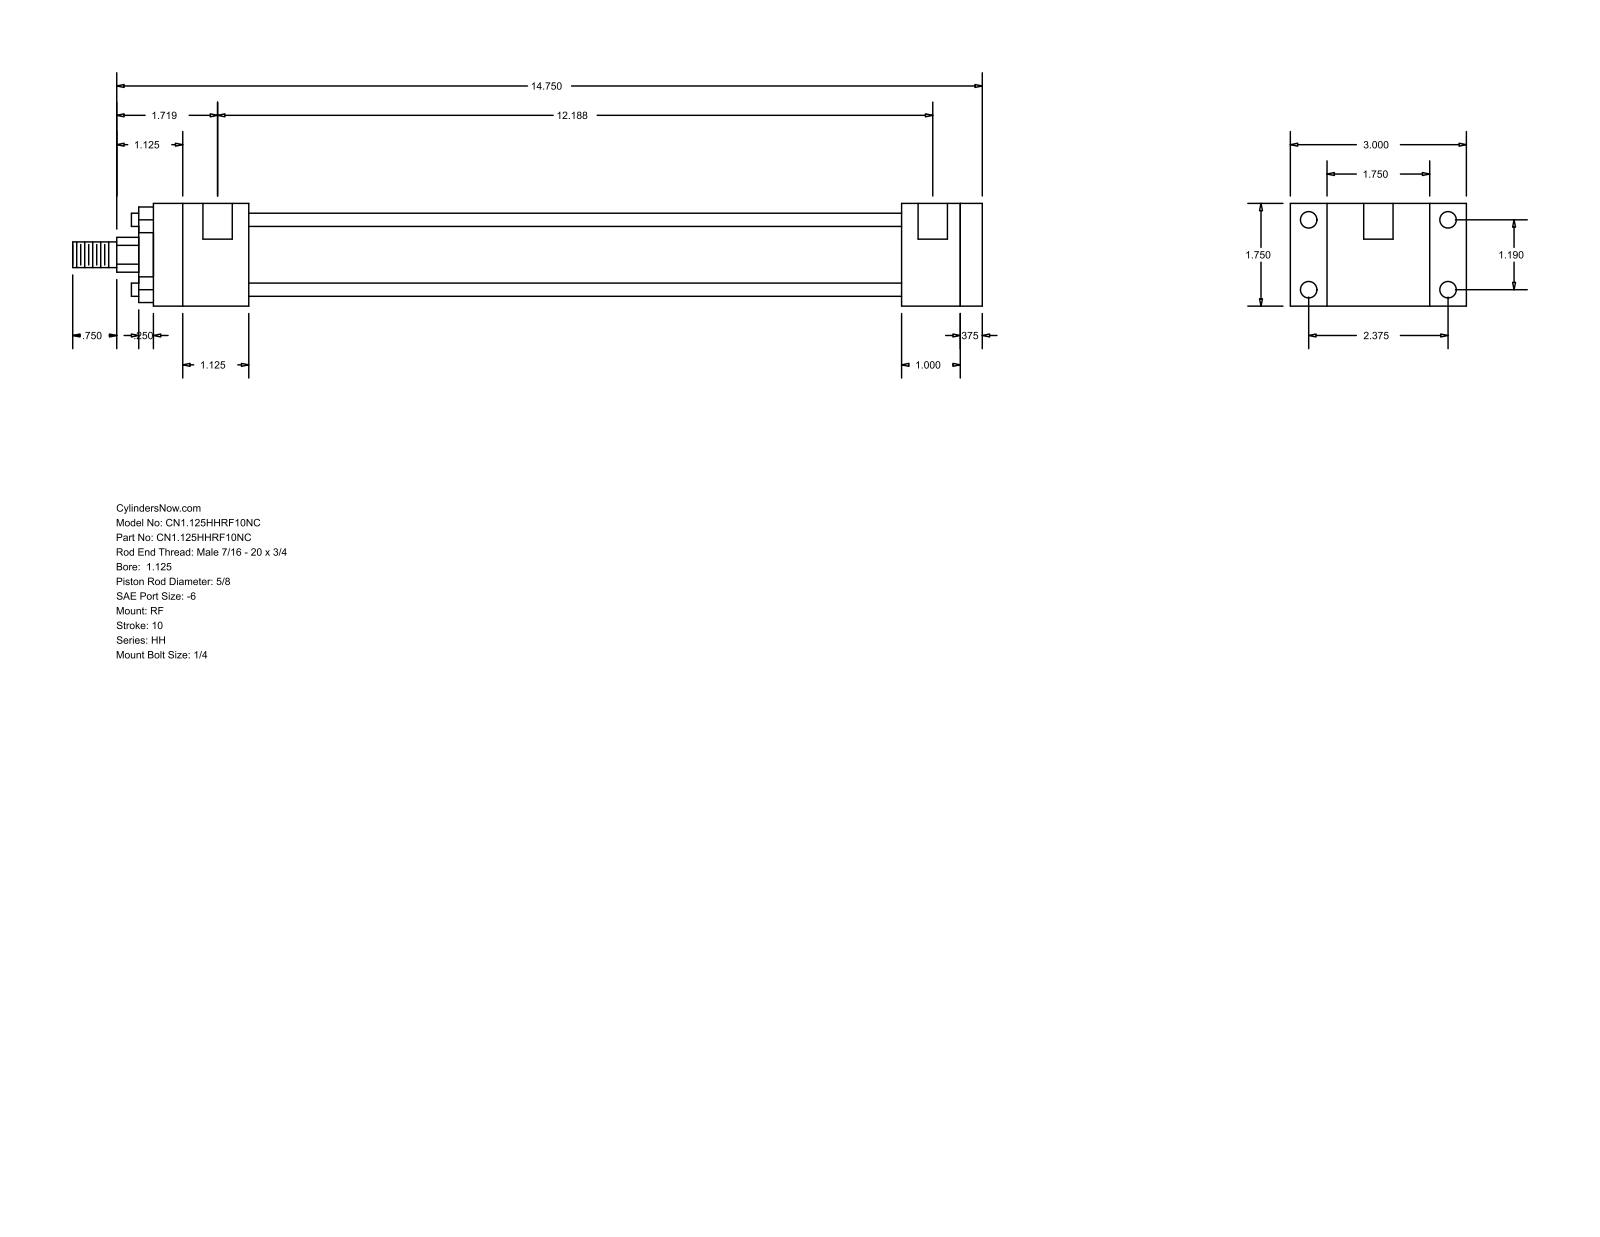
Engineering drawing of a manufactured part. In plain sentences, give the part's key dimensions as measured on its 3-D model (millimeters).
The part is named "HH_RF__0112_0.625". Its 3-D file was written by "GSSL Pune (CONFIG_CONTROL_DESIGN)". It is 0 solids with 92 faces: 64 planar, 28 cylindrical and 0 other. Overall it measures 393.7 by 76.2 by 44.45 millimeters. Round holes: 4 of diameter 5.56, 4 of diameter 7.14, 2 of diameter 12.7. Round bosses or shafts: 4 of diameter 5.71, 1 of diameter 34.92, 1 of diameter 28.57, 1 of diameter 15.88, 1 of diameter 11.11. Partial cylindrical surfaces (rounded edges, fillets, slot ends): 1 of radius 7.54. The main face-to-face distances are 44.46, 9.53, 358.77, 15.87, 307.97, 317.5, 282.58, 25.39, 34.92, 41.27. The hole center spacings are 30.22, 60.32, 67.47, 306.39, 3.17, 309.56.
